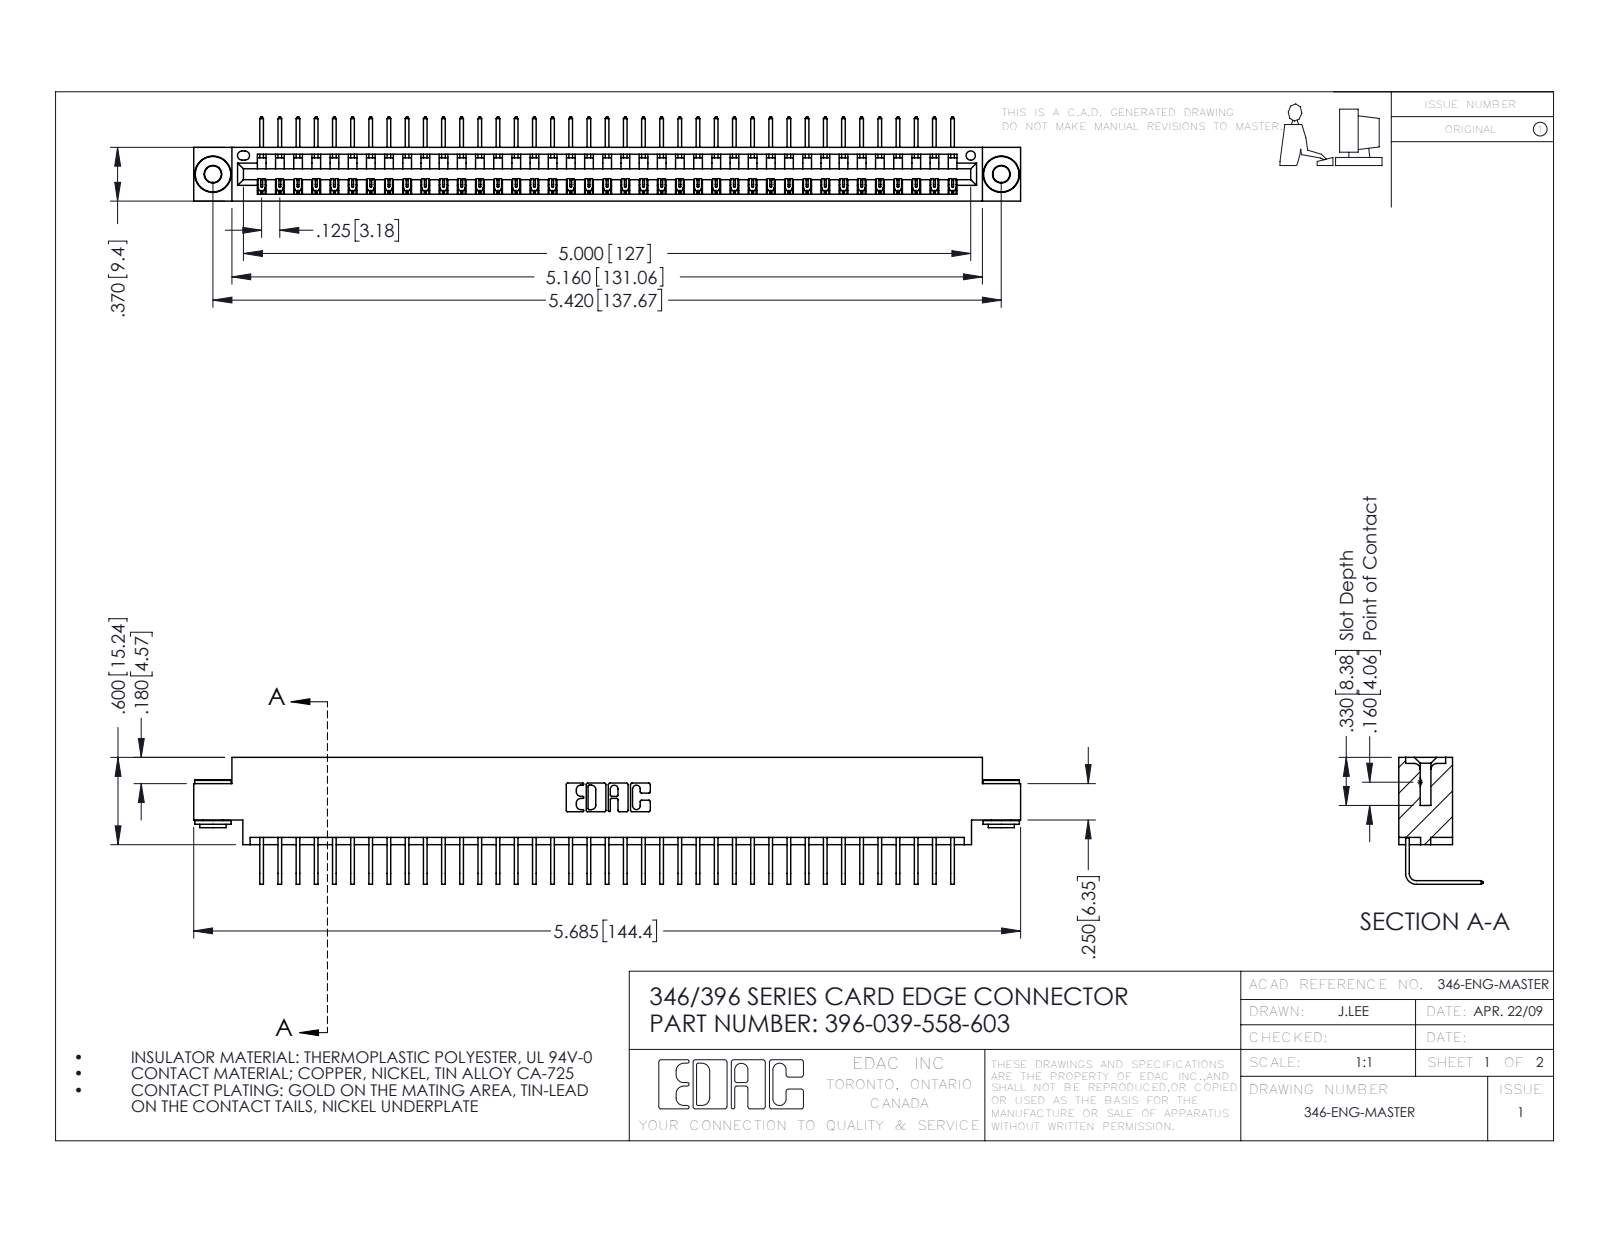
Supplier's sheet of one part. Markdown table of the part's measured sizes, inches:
| quantity | value |
| --- | --- |
| part name | 346 Part_0.170 Offset - 0.156 Dia-TH; 345-250-002_345-250-002-102; 345-292-001_558 Tail - 2; 396-039-558-603 |
| STEP written by | SolidWorks 2016 (CONFIG_CONTROL_DESIGN) |
| units | inches |
| bodies | 42 solids, 2504 faces (1728 planar, 768 cylindrical, 8 other) |
| overall size | 5.685 × 0.873 × 0.58 |
| volume | 0.842 in³ |
| surface area | 28.47 in² |
| round holes (diameter × count) | 0.116 × 2, 0.156 × 2, 0.064 × 1 |
| round bosses / shafts (diameter × count) | 0.25 × 2, 0.18 × 2, 0.136 × 2 |
| partial cylindrical surfaces (radius × count) | 0.006 × 78, 0.01 × 22, 0.007 × 6, 0.031 × 6, 0.026 × 3, 0.031 × 2, 0.04 × 2, 0.014 × 1 |
| main face-to-face distances | 0.322, 0.048, 0.37, 0.25, 0.025, 0.298, 0.072, 0.148, 0.222, 0.1 |
| hole center spacings | 0.246, 5.211, 5.42 |
